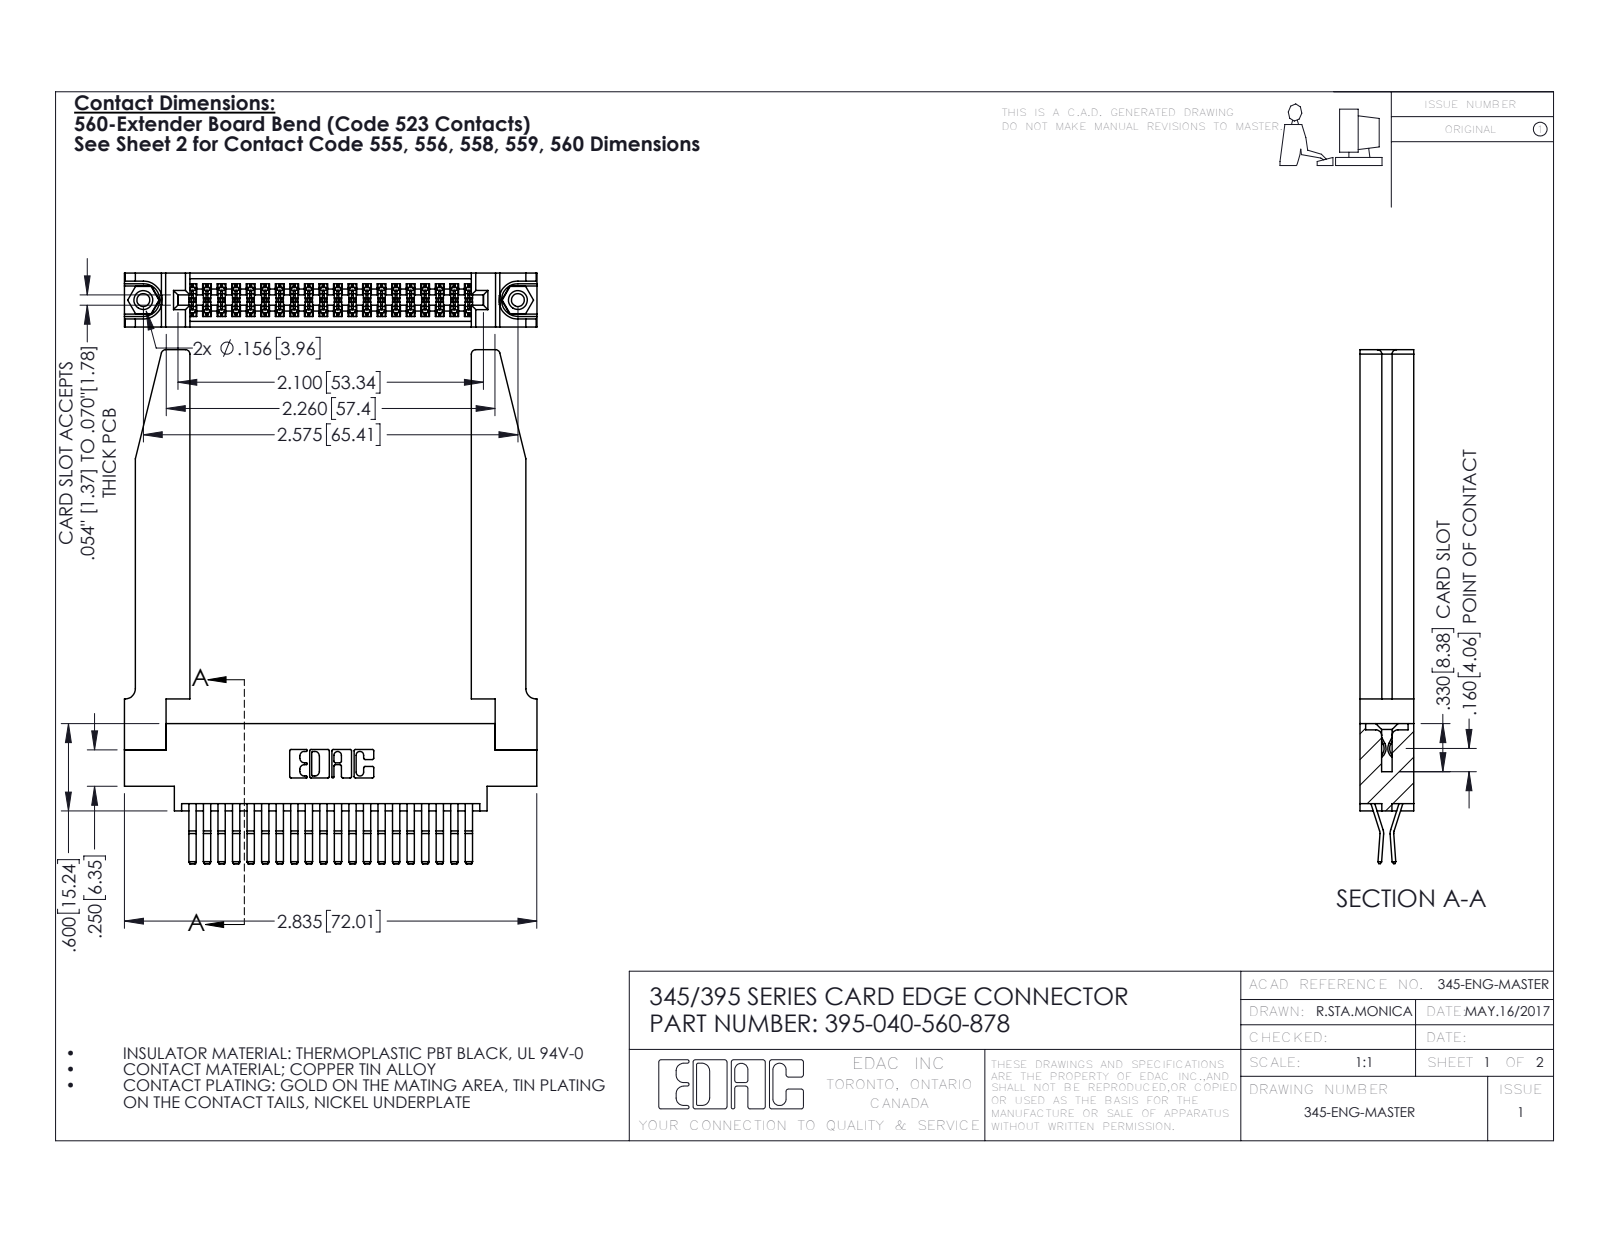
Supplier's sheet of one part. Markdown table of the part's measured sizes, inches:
| quantity | value |
| --- | --- |
| part name | 395-040-560-878; 345-220-078_345-220-078; 345-250-001_345-250-001-102; 345-292-001_560 Tail (+1 more) |
| STEP written by | SolidWorks 2016 (CONFIG_CONTROL_DESIGN) |
| units | inches |
| bodies | 45 solids, 2444 faces (1546 planar, 846 cylindrical, 52 other) |
| overall size | 3.532 × 2.836 × 0.37 |
| volume | 0.898 in³ |
| surface area | 27.11 in² |
| round holes (diameter × count) | 0.089 × 2, 0.125 × 2, 0.156 × 2, 0.064 × 1 |
| round bosses / shafts (diameter × count) | 0.155 × 2 |
| partial cylindrical surfaces (radius × count) | 0.006 × 60, 0.01 × 22, 0.03 × 8, 0.007 × 6, 0.031 × 6, 0.026 × 3, 0.01 × 2, 0.014 × 2 |
| main face-to-face distances | 0.37, 0.072, 0.298, 0.025, 0.098, 0.272, 0.2, 0.148, 0.15, 0.225 |
| hole center spacings | 0.27, 2.341, 2.575 |
